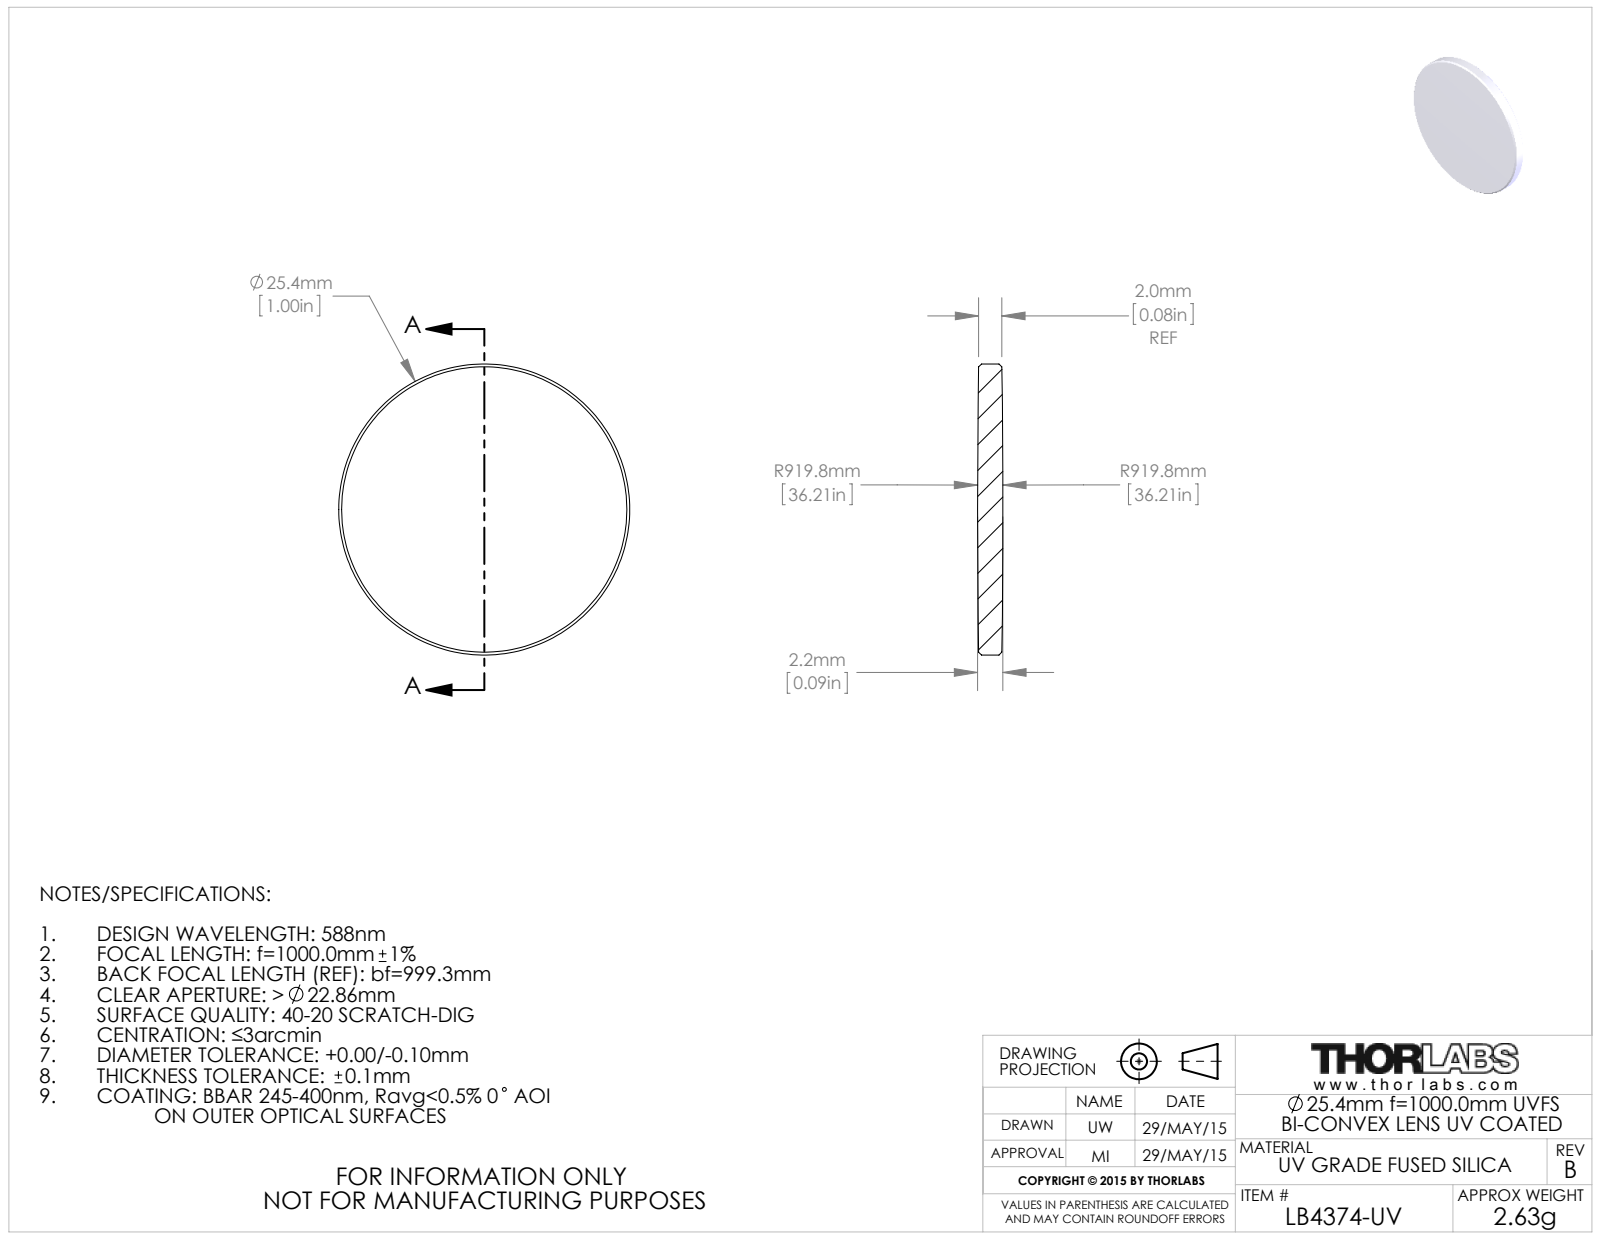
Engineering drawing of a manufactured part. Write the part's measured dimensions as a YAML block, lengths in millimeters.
part_name: "4330-E0W"
step_written_by: "SolidWorks 2014 (CONFIG_CONTROL_DESIGN)"
units: millimeters
bodies: {solids: 1, faces: 10, planar: 0, cylindrical: 2, other: 8}
overall_size: [25.4, 25.4, 2.2]
volume: 1065
surface_area: 1152
round_bosses_or_shafts:
  - {diameter: 25.4, count: 1}
